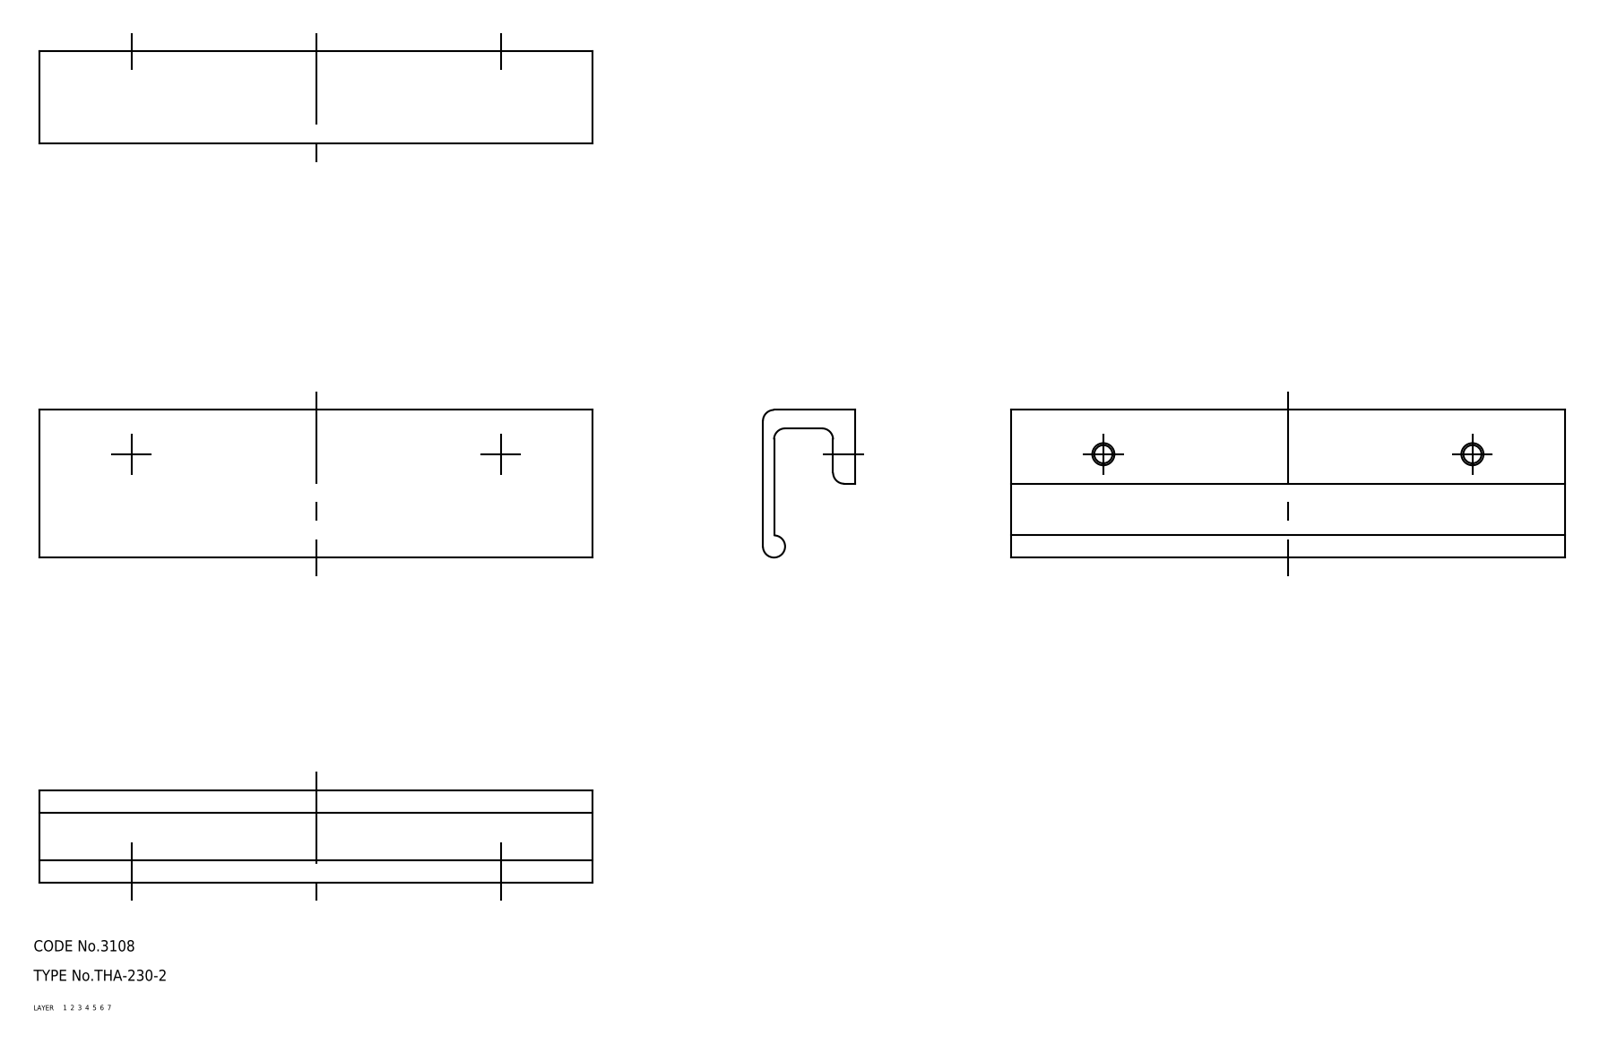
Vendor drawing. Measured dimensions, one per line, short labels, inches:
name: pull
written by: CADfix (AUTOMOTIVE_DESIGN)
unit: in
bodies: 1 solid, 18 faces (0 planar, 0 cylindrical, 18 other)
size: 5.906 × 1.575 × 0.984
volume: 3.02 in³; area: 37.71 in²
